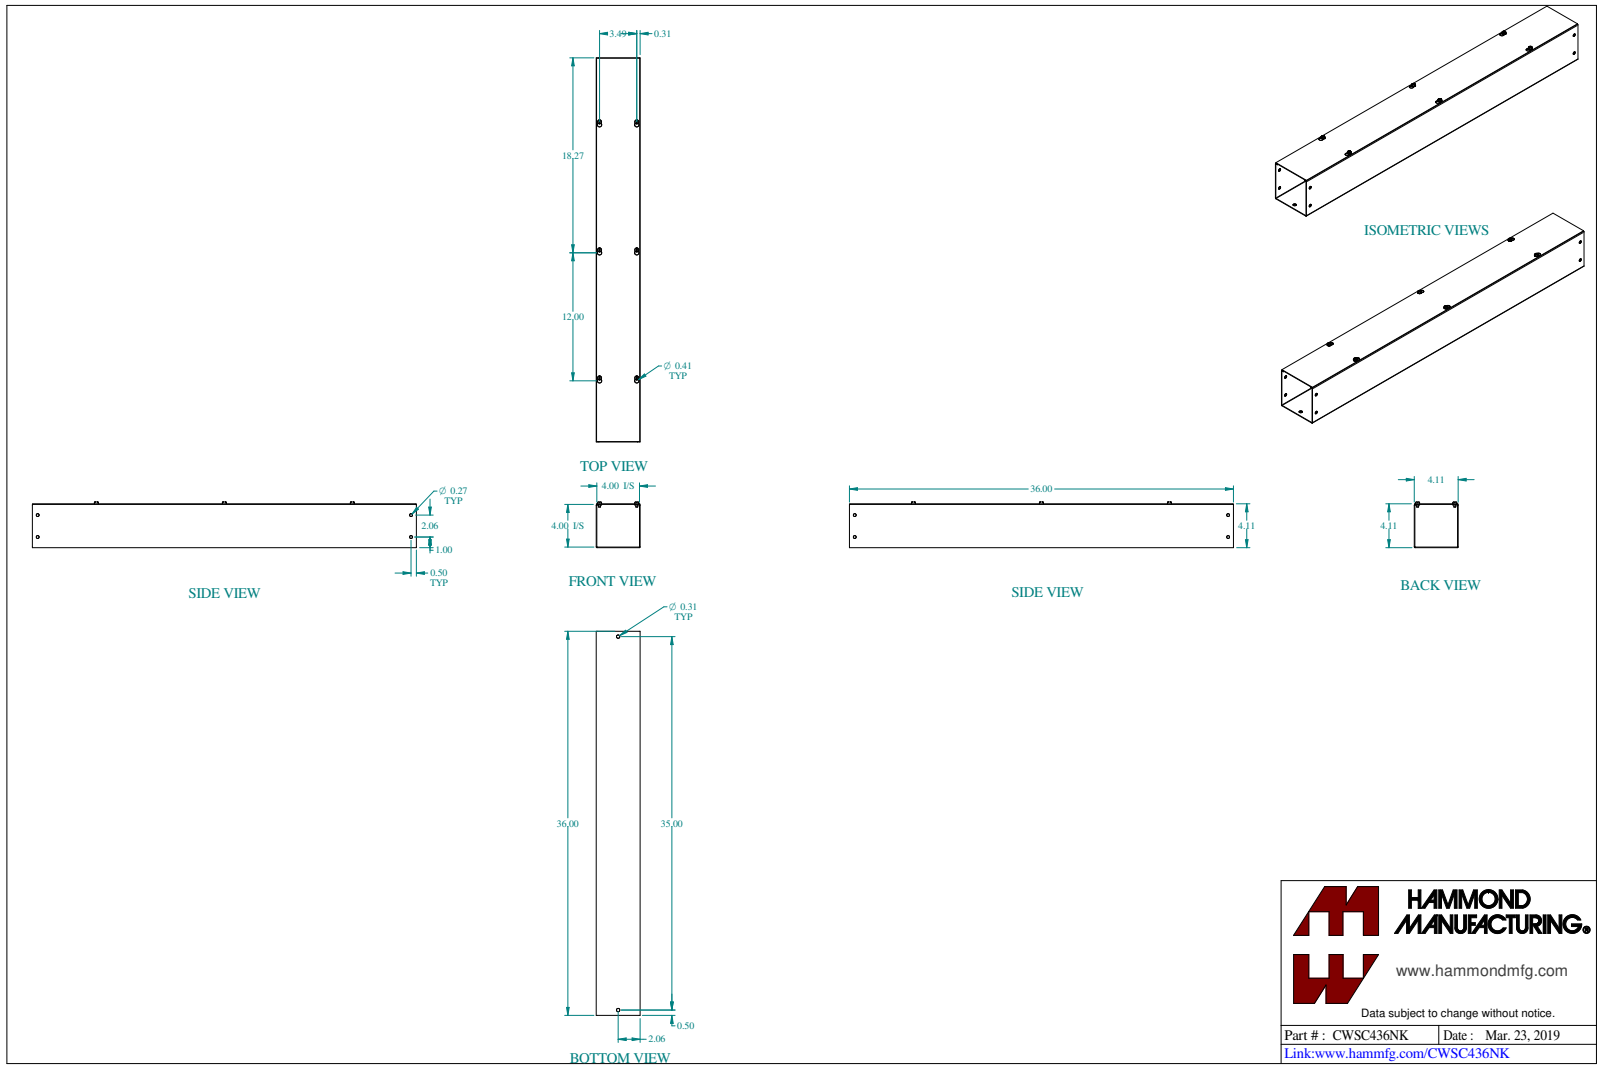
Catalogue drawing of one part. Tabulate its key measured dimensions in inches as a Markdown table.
| quantity | value |
| --- | --- |
| part name | CWSC436NK |
| STEP written by | SolidWorks 2023 (CONFIG_CONTROL_DESIGN) |
| units | inches |
| bodies | 8 solids, 242 faces (118 planar, 88 cylindrical, 36 other) |
| overall size | 36 × 4.289 × 4.114 |
| volume | 34.76 in³ |
| surface area | 1 229 in² |
| round holes (diameter × count) | 0.177 × 6, 0.266 × 4, 0.313 × 2 |
| round bosses / shafts (diameter × count) | 0.375 × 6, 0.19 × 6 |
| partial cylindrical surfaces (radius × count) | 0.125 × 6, 0.203 × 6, 0.029 × 4, 0.086 × 4 |
| main face-to-face distances | 0.057, 4.057, 4, 4.114, 3.943, 0.114, 0.031, 4.083, 0.026, 4.026 |
| hole center spacings | 5.77, 12, 12.497, 17.587, 29.552, 3.489, 35, 2.057 |
